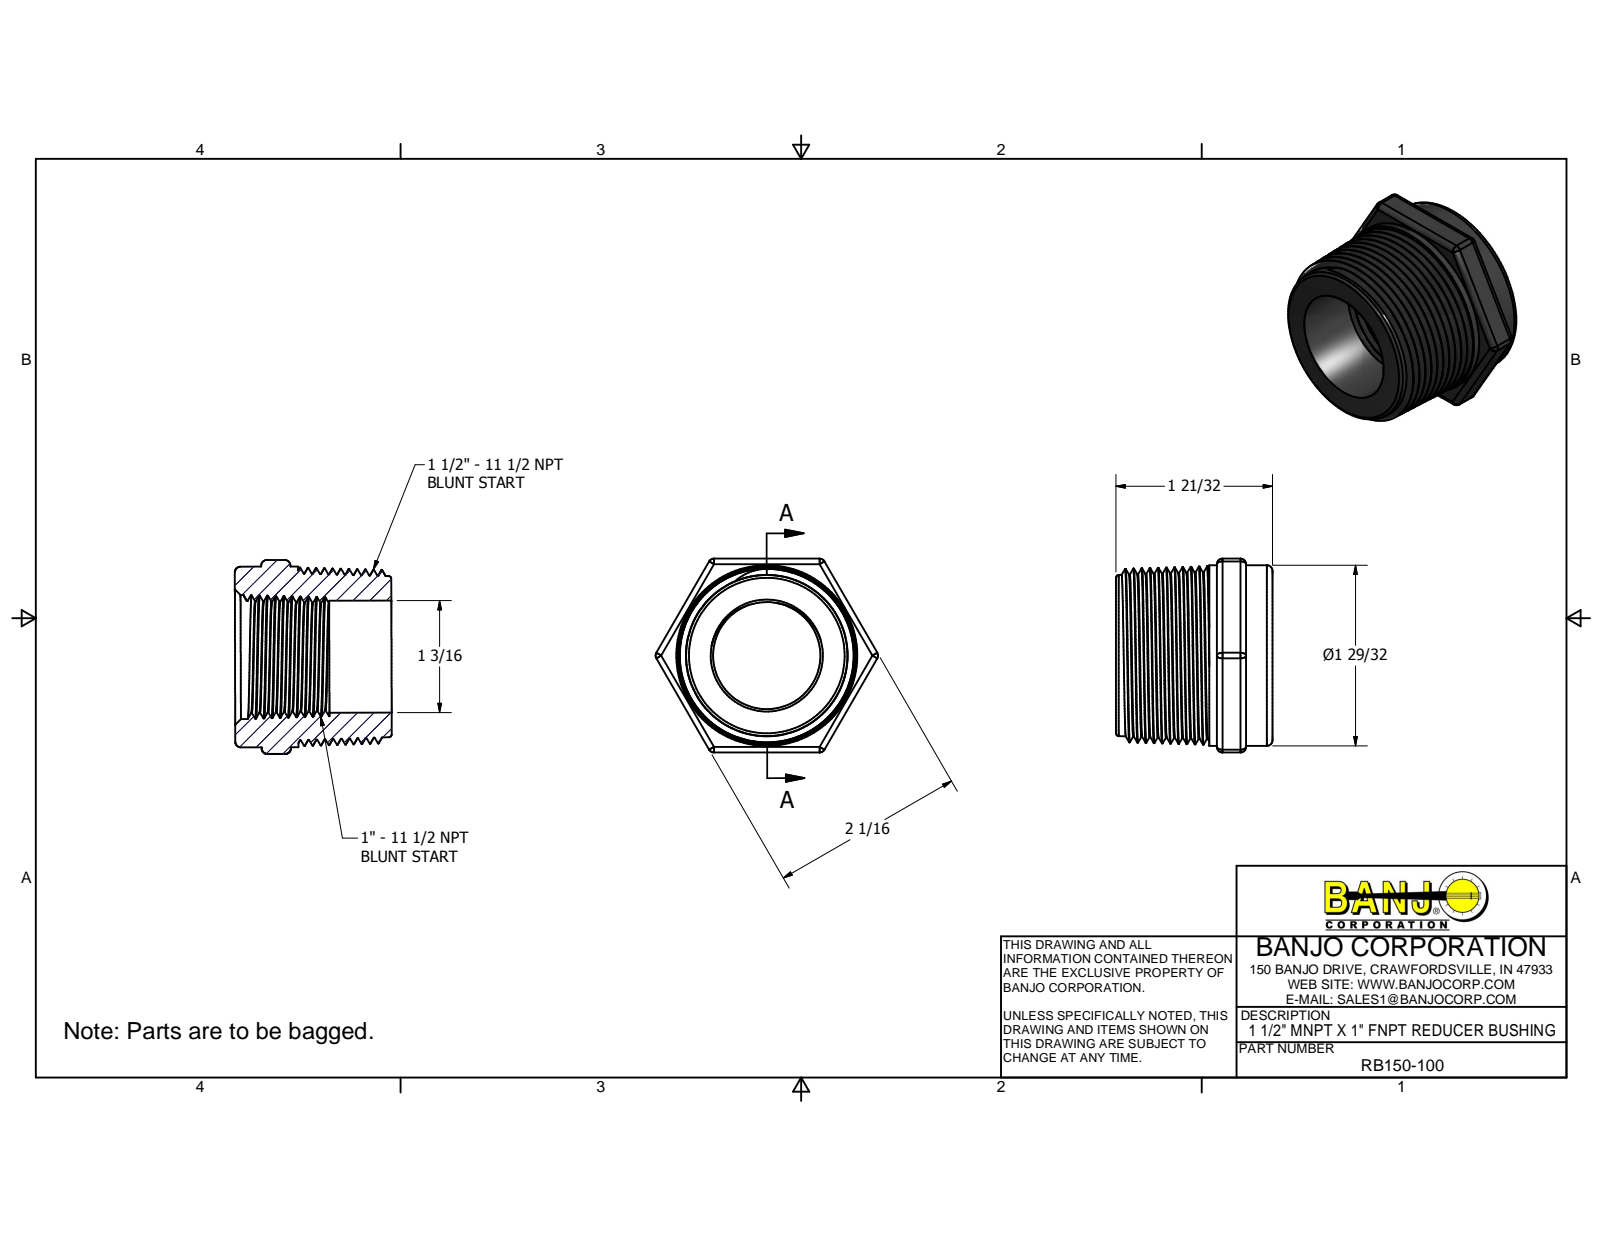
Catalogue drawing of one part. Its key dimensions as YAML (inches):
part_name: "RB150-100"
step_written_by: "Autodesk Inventor 2014 (AUTOMOTIVE_DESIGN)"
units: inches
bodies: {solids: 1, faces: 83, planar: 13, cylindrical: 23, other: 47}
overall_size: [2.36, 2.06, 1.66]
volume: 2.725
surface_area: 27.23
round_holes:
  - {diameter: 1.19, count: 1}
round_bosses_or_shafts:
  - {diameter: 1.92, count: 1}
partial_cylinders:
  - {radius: 0.06, count: 18}
  - {radius: 0.394, count: 1}
  - {radius: 0.493, count: 1}
face_to_face_distances: [1.66, 2.06, 0.28, 0.59, 0.31, 1.38, 1.07, 0.67, 0.39, 0.08]
